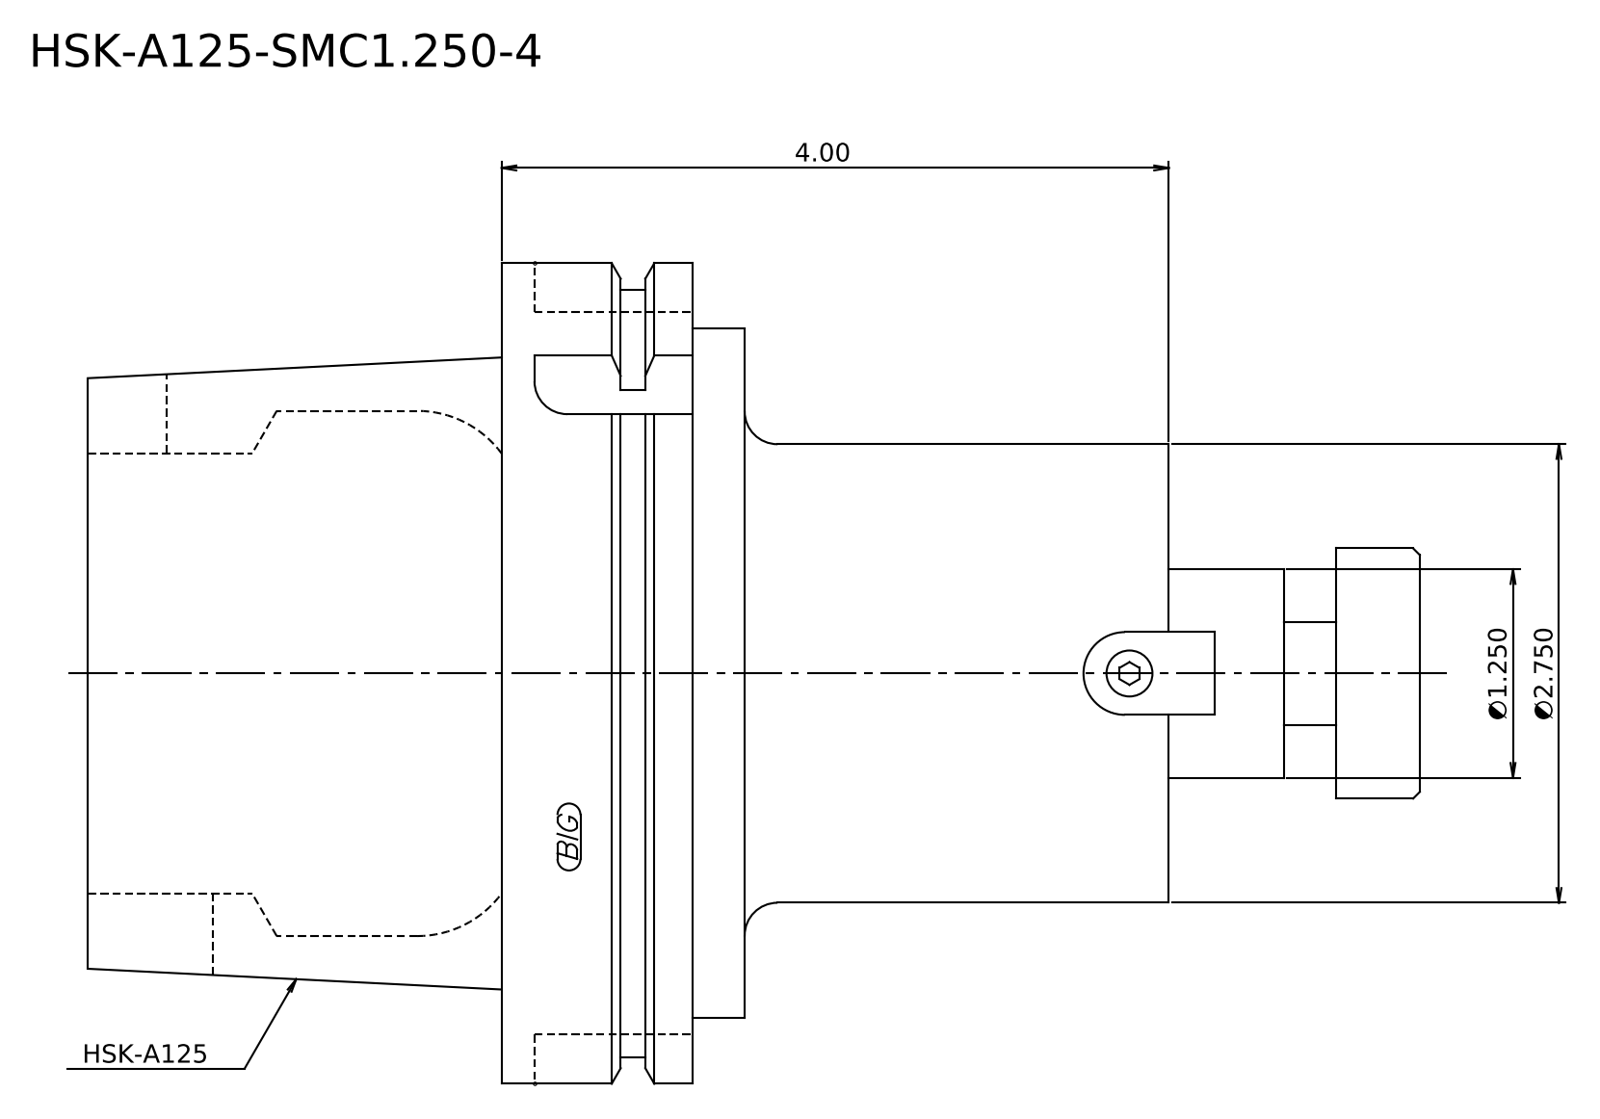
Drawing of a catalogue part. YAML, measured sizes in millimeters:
step_written_by: "Kubotek KeyCreator 2011 V10.0.2 (22737) (automotive_design)"
units: millimeters
bodies: {solids: 1, faces: 18, planar: 8, cylindrical: 6, other: 4}
overall_size: [182.1, 125, 125]
volume: 1112000
surface_area: 73563
round_bosses_or_shafts:
  - {diameter: 125, count: 1}
  - {diameter: 117, count: 1}
  - {diameter: 105, count: 1}
  - {diameter: 69.85, count: 1}
  - {diameter: 31.75, count: 1}
face_to_face_distances: [63, 37, 100, 8, 29, 92, 64.6, 72.6, 101.6, 164.6]
